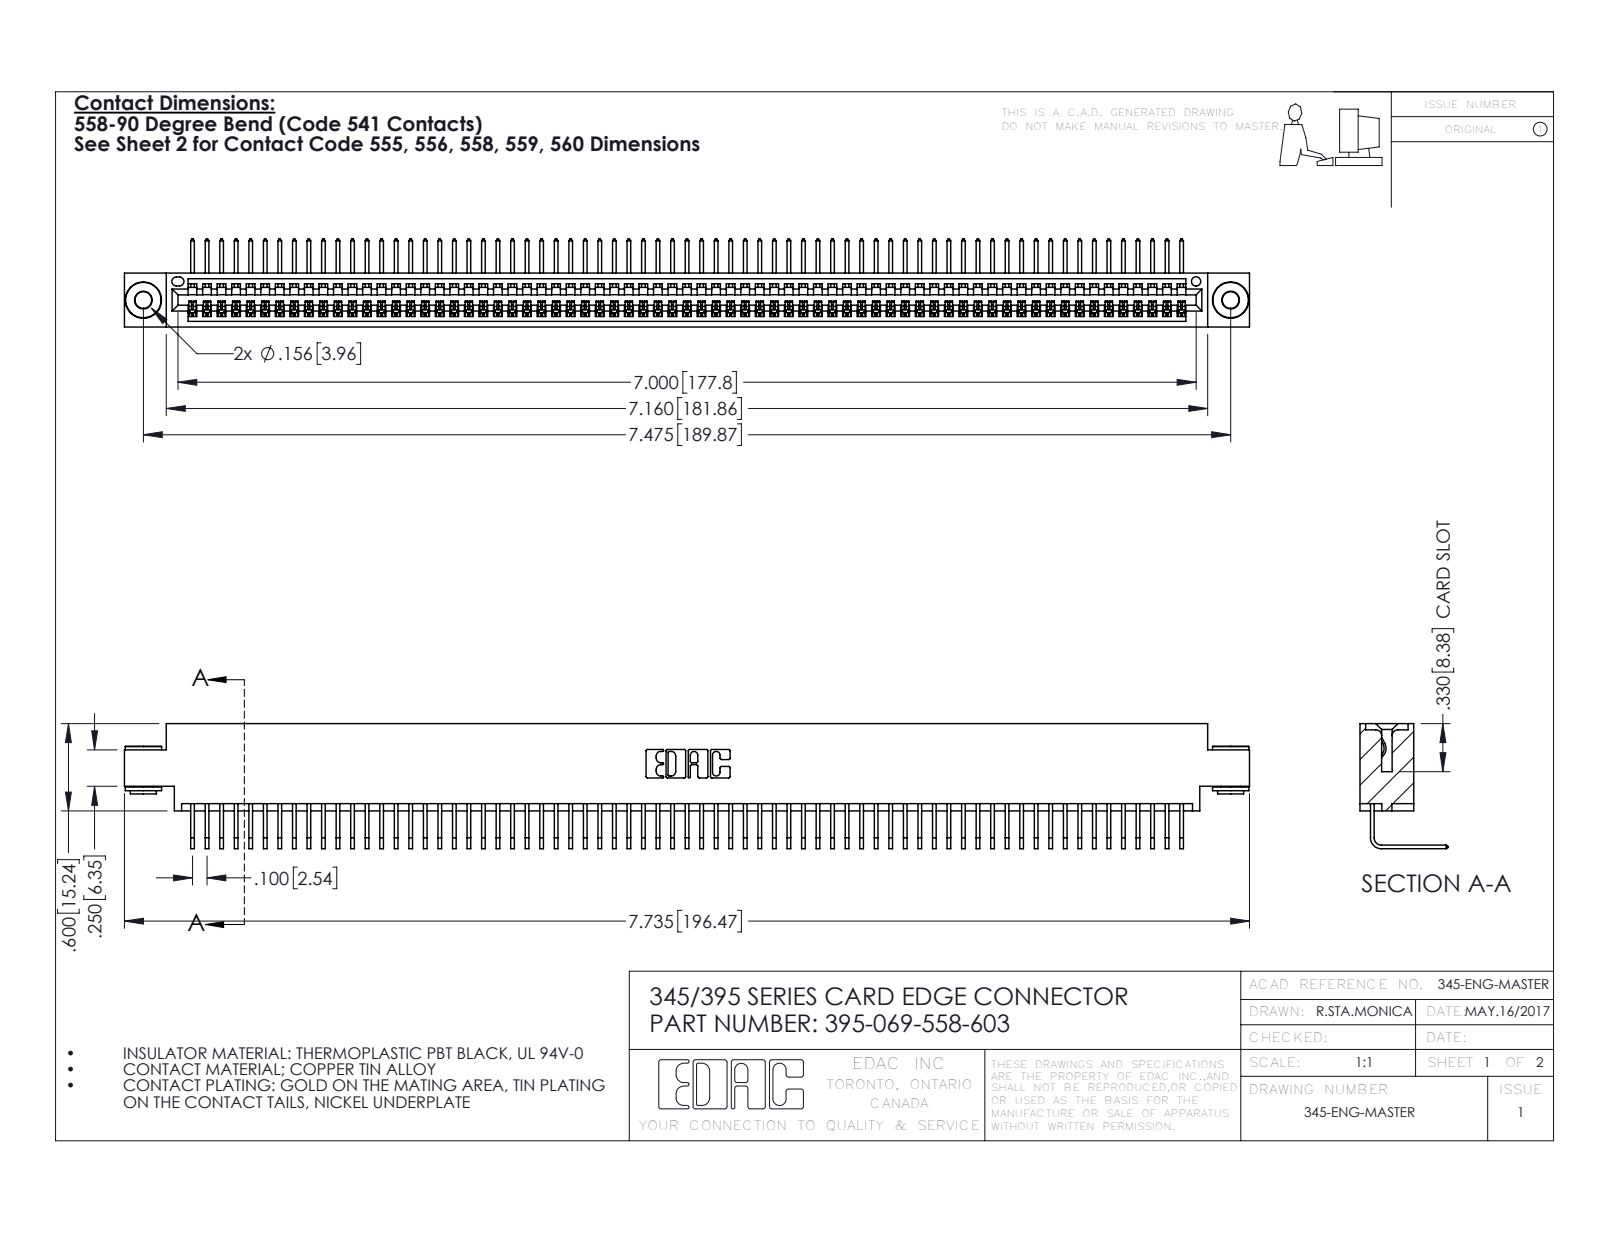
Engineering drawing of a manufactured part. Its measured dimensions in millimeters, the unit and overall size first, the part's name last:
Units: millimetres
Overall size (bounding box): 196.5 × 21.8 × 15.4
Round holes (diameter × count): ⌀2.9 ×2, ⌀4 ×2, ⌀1.6 ×1
Round bosses / shafts (diameter × count): ⌀6.4 ×2, ⌀4.6 ×2, ⌀3.5 ×2
Partial cylindrical surfaces — rounded edges, fillets, slot ends (radius × count): R0.2 ×138, R0.3 ×22, R0.2 ×6, R0.8 ×6, R0.7 ×3, R0.8 ×2, R1 ×2, R0.4 ×1
Main face-to-face distances: 1.8, 7.6, 9.4, 5.1, 2.5, 6.9, 0.6, 5.7, 4.4, 3.8
Hole centre spacings: 6.9, 183.9, 189.9
Volume: 19 030 mm³ · Surface area: 27 330 mm²
Bodies: 72 solids, 4308 faces (2992 planar, 1308 cylindrical, 8 other)
Part name (STEP PRODUCT): 395-069-558-603; 345 Part_0.170 Offset - 0.156 Dia-TH; 345-292-001_558 Tail - 2; 345-250-002_345-250-002-102
STEP written by: SolidWorks 2016 (CONFIG_CONTROL_DESIGN)
